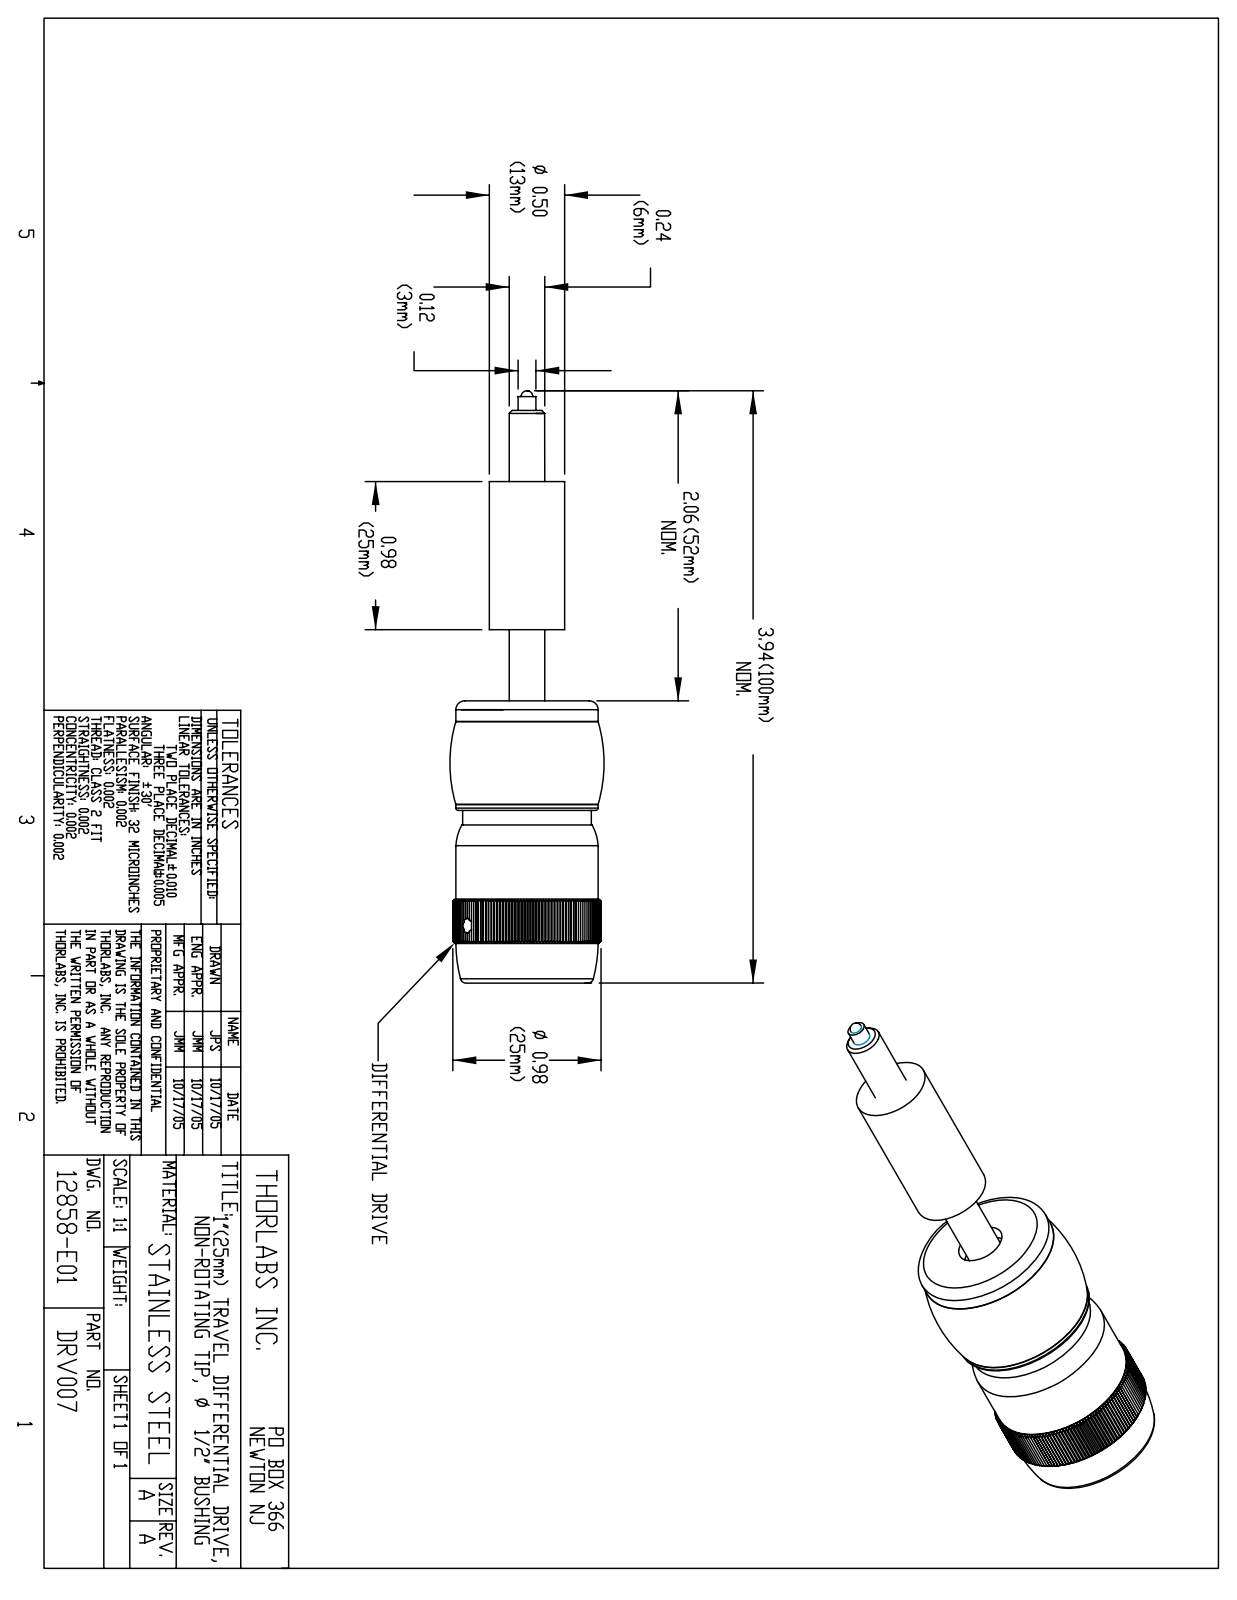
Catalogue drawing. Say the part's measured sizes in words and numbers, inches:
The part is named "12858-E0W". Its 3-D file was written by "SolidWorks 2007 (AUTOMOTIVE_DESIGN)". It is 0 solids with 355 faces: 305 planar, 20 cylindrical and 30 other. Overall it measures 3.936 by 1.024 by 1.024 inches. Round holes: 1 of diameter 0.098, 1 of diameter 0.315, 1 of diameter 0.866. Round bosses or shafts: 1 of diameter 0.945, 1 of diameter 0.854, 1 of diameter 0.5, 1 of diameter 0.236, 1 of diameter 0.118. The main face-to-face distances are 0.681, 0.68, 0.472, 1.457, 0.984, 0.681, 0.728, 1.201, 2.185, 0.63.
